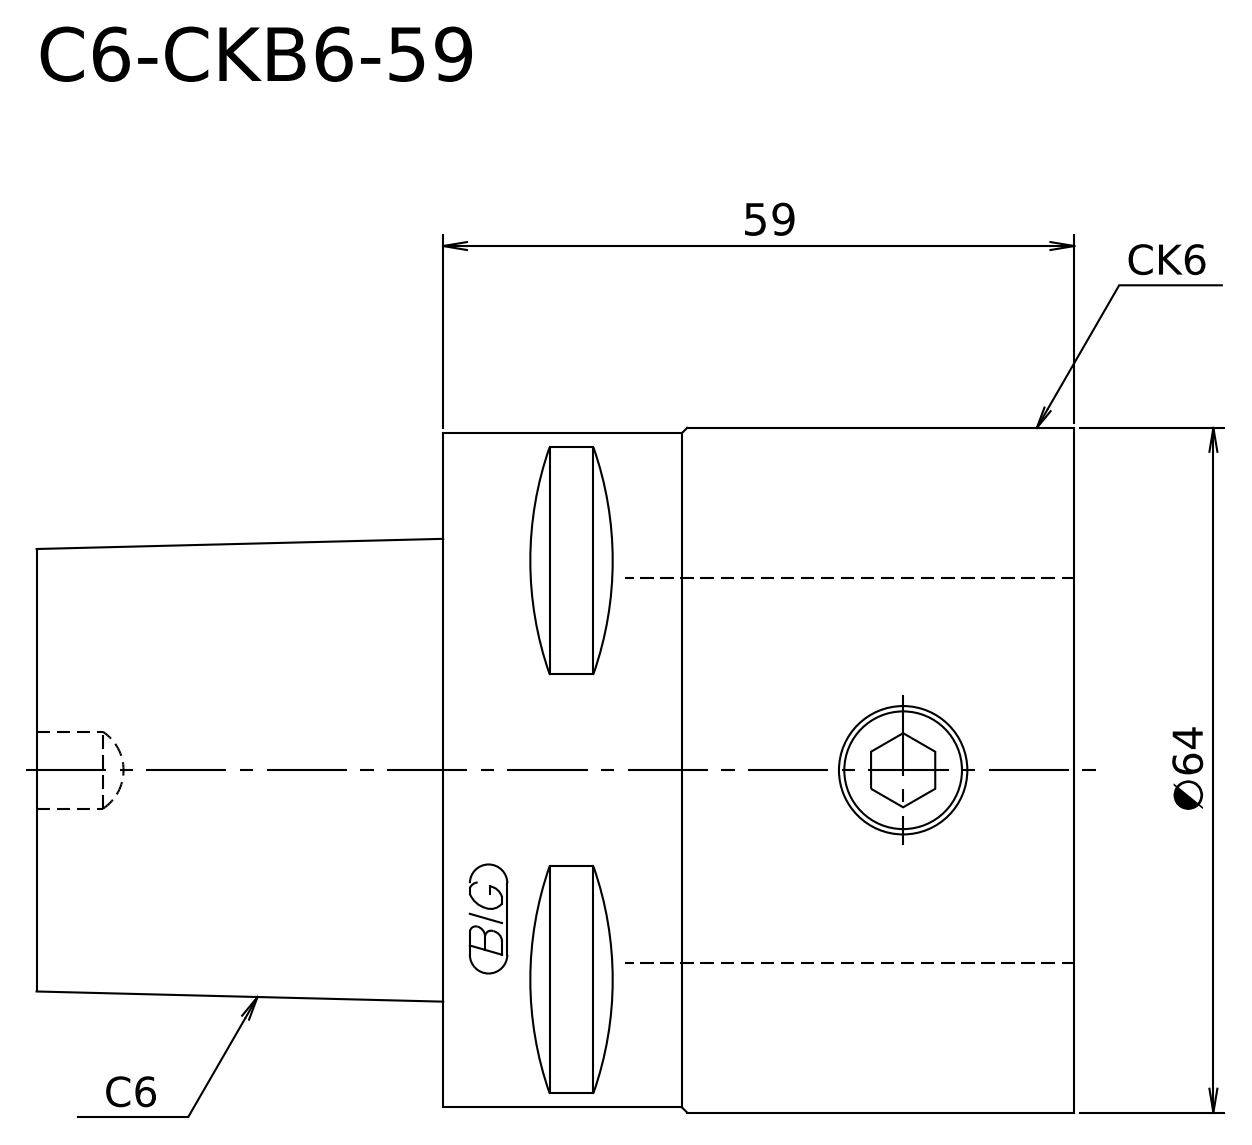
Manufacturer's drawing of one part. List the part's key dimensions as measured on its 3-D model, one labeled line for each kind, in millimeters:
STEP written by: Kubotek KeyCreator V8.5.1 (14335) (CONFIG_CONTROL_DESIGN)
Units: millimetres
Bodies: 1 solid, 9 faces (3 planar, 2 cylindrical, 4 other)
Overall size (bounding box): 97 × 64 × 64
Volume: 242 307 mm³ · Surface area: 23 195 mm²
Round bosses / shafts (diameter × count): ⌀64 ×1, ⌀62.98 ×1
Main face-to-face distances: 59, 97, 38
